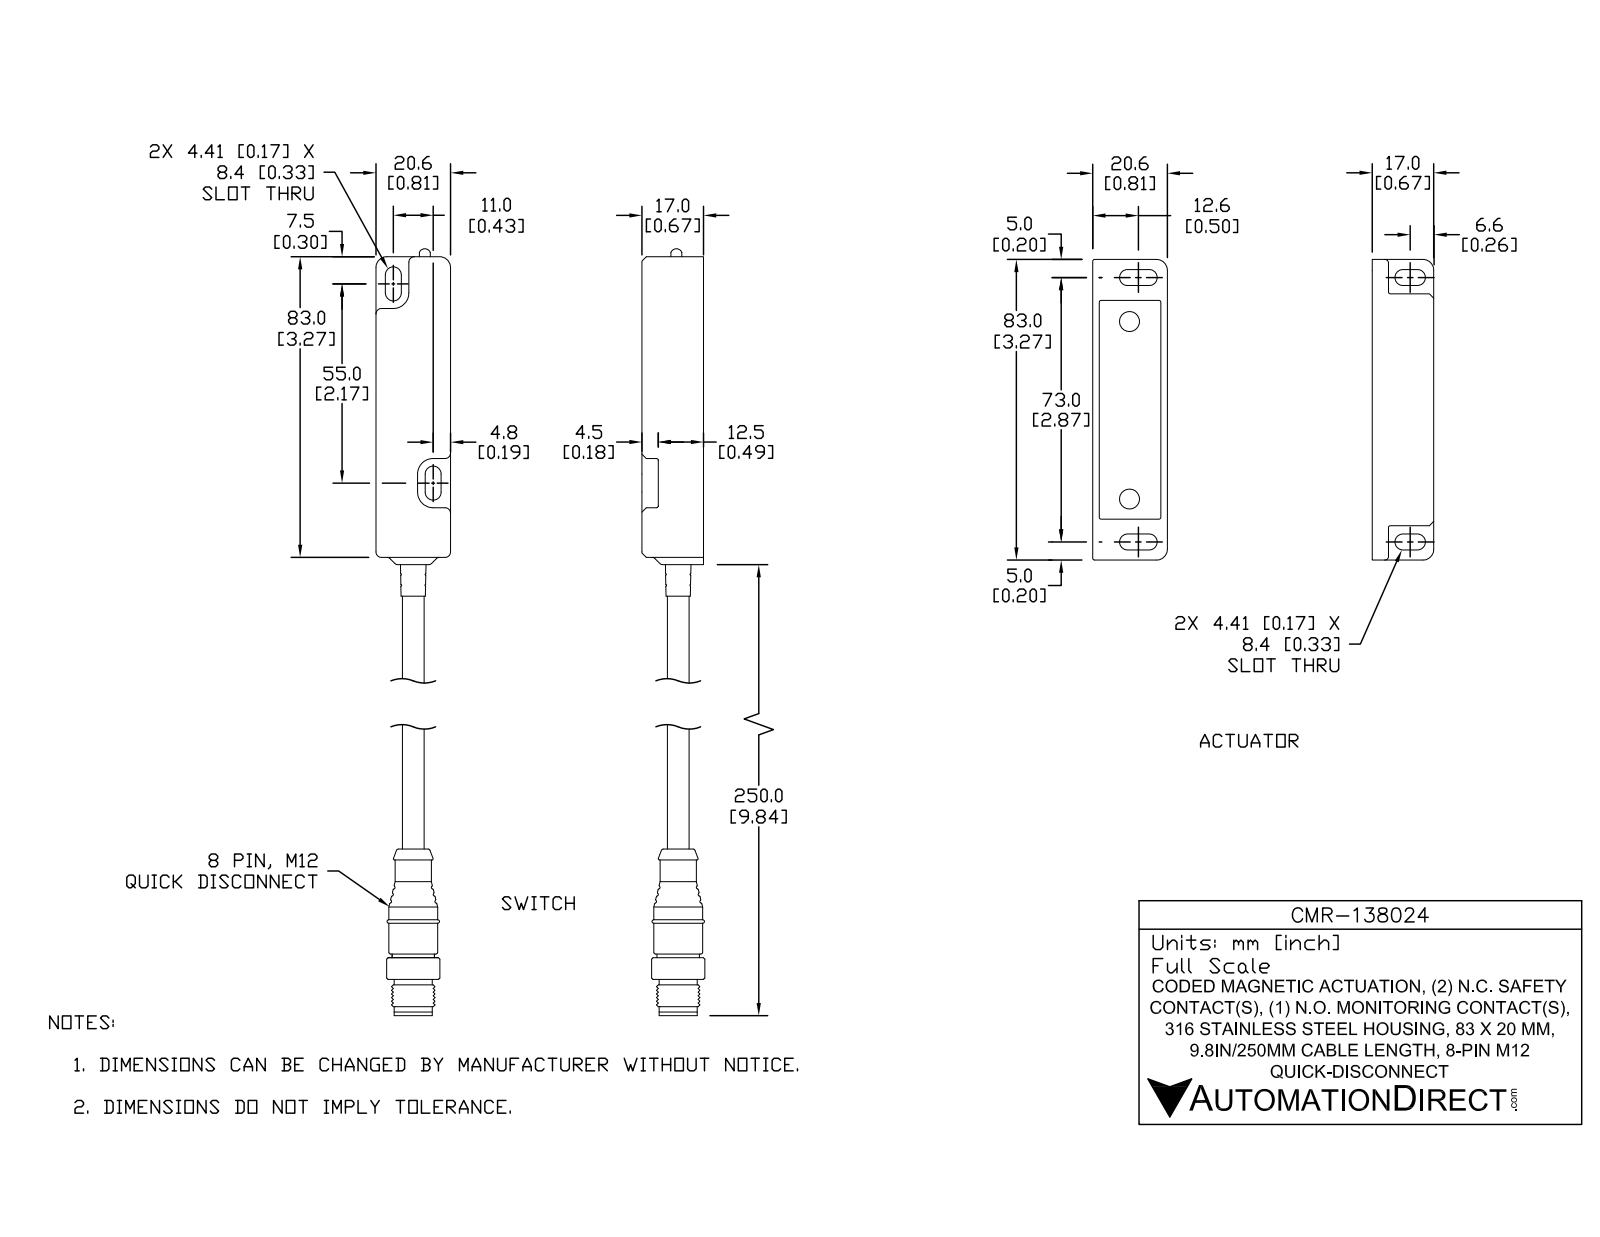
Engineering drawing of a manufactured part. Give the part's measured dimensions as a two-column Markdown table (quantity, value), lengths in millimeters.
| quantity | value |
| --- | --- |
| part name | CMR-138024; CMR-138024_1; CMR-138024_2 |
| STEP written by | SolidWorks 2017 (AUTOMOTIVE_DESIGN) |
| units | millimeters |
| bodies | 11 solids, 1009 faces (372 planar, 350 cylindrical, 287 other) |
| overall size | 335 × 42.2 × 17.3 |
| volume | 37 000 mm³ |
| surface area | 36 300 mm² |
| round holes (diameter × count) | 5 × 4, 4.2 × 1, 5.9 × 1, 7.2 × 1, 8.3 × 1, 11.8 × 1 |
| round bosses / shafts (diameter × count) | 0.8 × 8, 4.9 × 4, 2 × 4, 13.5 × 1, 11.7 × 1, 10.5 × 1, 10 × 1, 9.5 × 1 |
| partial cylindrical surfaces (radius × count) | 0.5 × 94, 0.3 × 15, 2.2 × 12, 1 × 10, 1.5 × 6, 3 × 6, 0.2 × 4, 0.7 × 3 |
| main face-to-face distances | 1.8, 21.6, 18.8, 17, 20.6, 40.4, 19.8, 16.8, 2, 14.8 |
| hole center spacings | 1.3, 27.1, 27.4, 28.4, 49, 63.1, 64.3, 65.6 |
